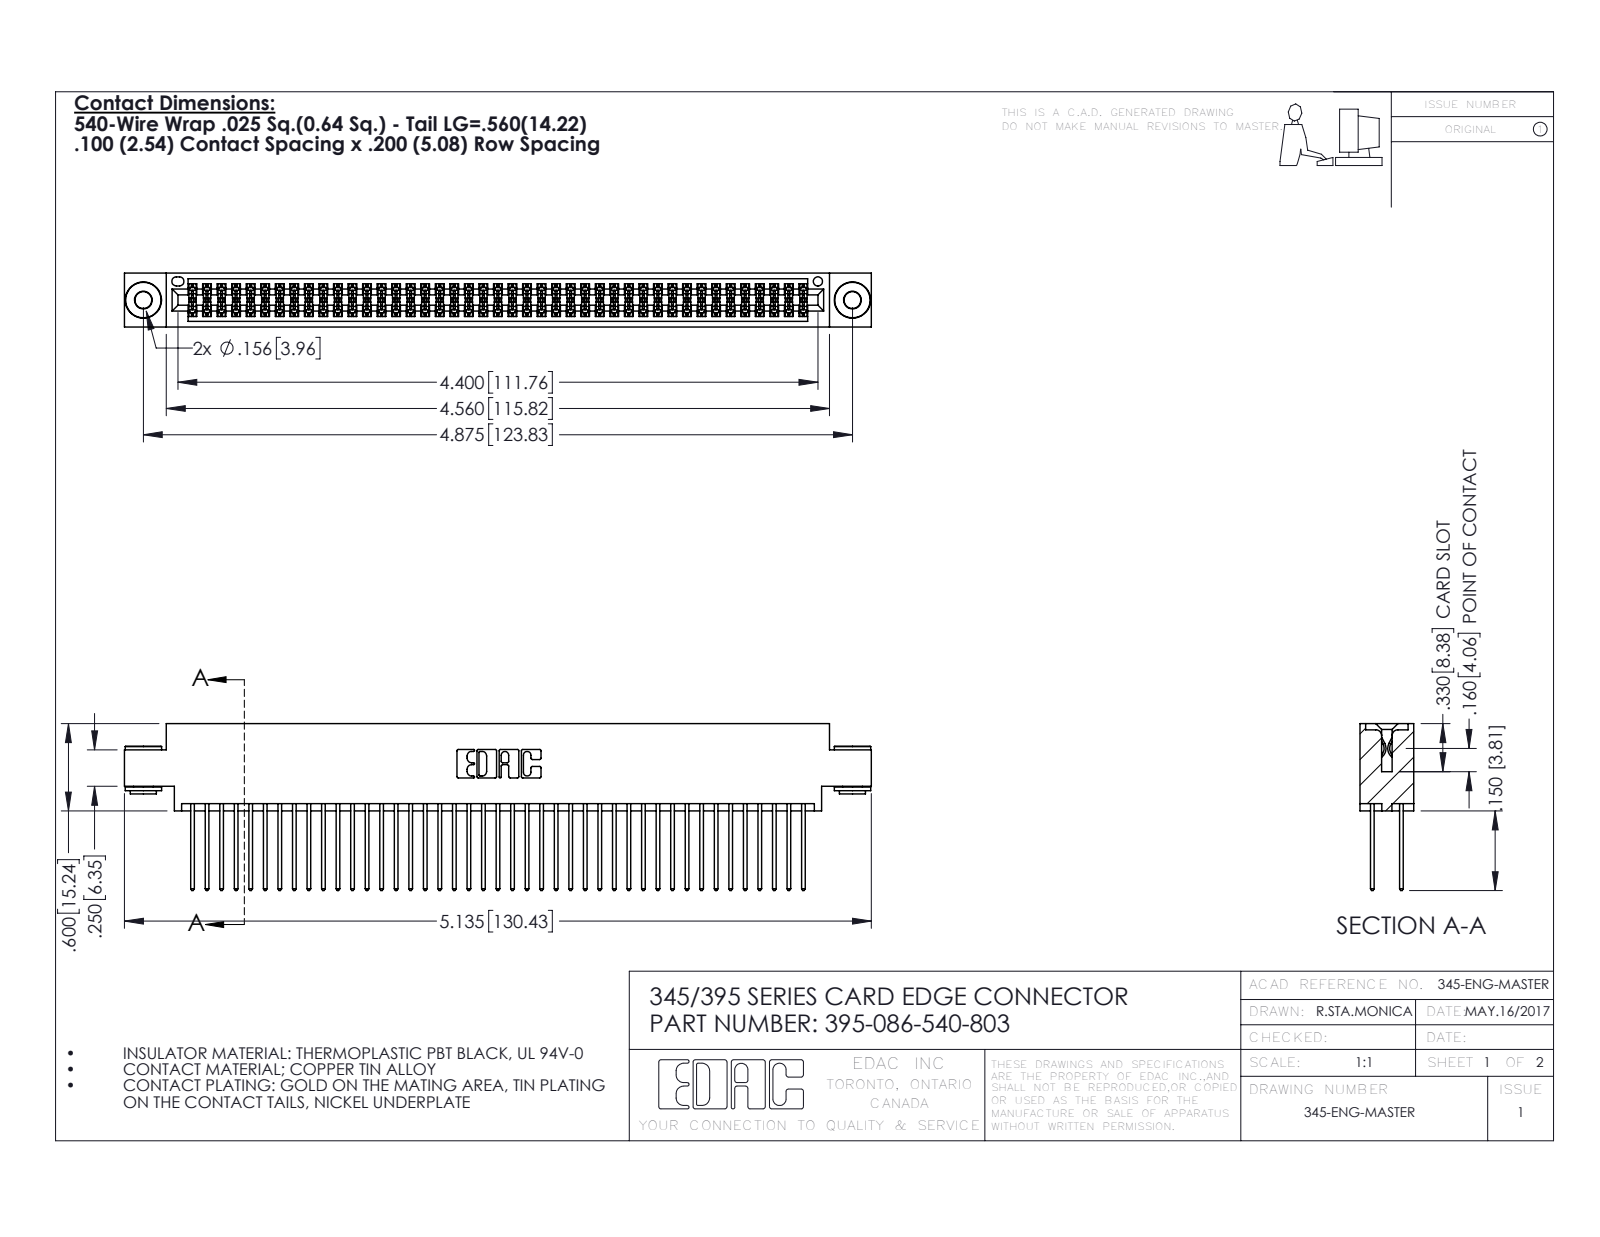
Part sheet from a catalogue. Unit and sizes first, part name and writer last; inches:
Units: inches
Overall size (bounding box): 5.135 × 1.147 × 0.37
Round holes (diameter × count): ⌀0.116 ×2, ⌀0.156 ×2, ⌀0.064 ×1
Round bosses / shafts (diameter × count): ⌀0.25 ×2, ⌀0.18 ×2, ⌀0.136 ×2
Partial cylindrical surfaces — rounded edges, fillets, slot ends (radius × count): R0.006 ×129, R0.01 ×86, R0.01 ×22, R0.007 ×6, R0.031 ×6, R0.026 ×3, R0.014 ×2, R0.019 ×2
Main face-to-face distances: 0.072, 0.298, 0.2, 0.098, 0.272, 0.025, 0.37, 0.225, 0.175, 0.149
Hole centre spacings: 0.27, 4.639, 4.875
Volume: 0.788 in³ · Surface area: 32.5 in²
Bodies: 89 solids, 4468 faces (2932 planar, 1528 cylindrical, 8 other)
Part name (STEP PRODUCT): 345-292-001_345-293-140; 395-086-540-803; 345-250-002_345-250-002-102; 345 Part_0.170 Offset - 0.156 Dia-TH
STEP written by: SolidWorks 2016 (CONFIG_CONTROL_DESIGN)
